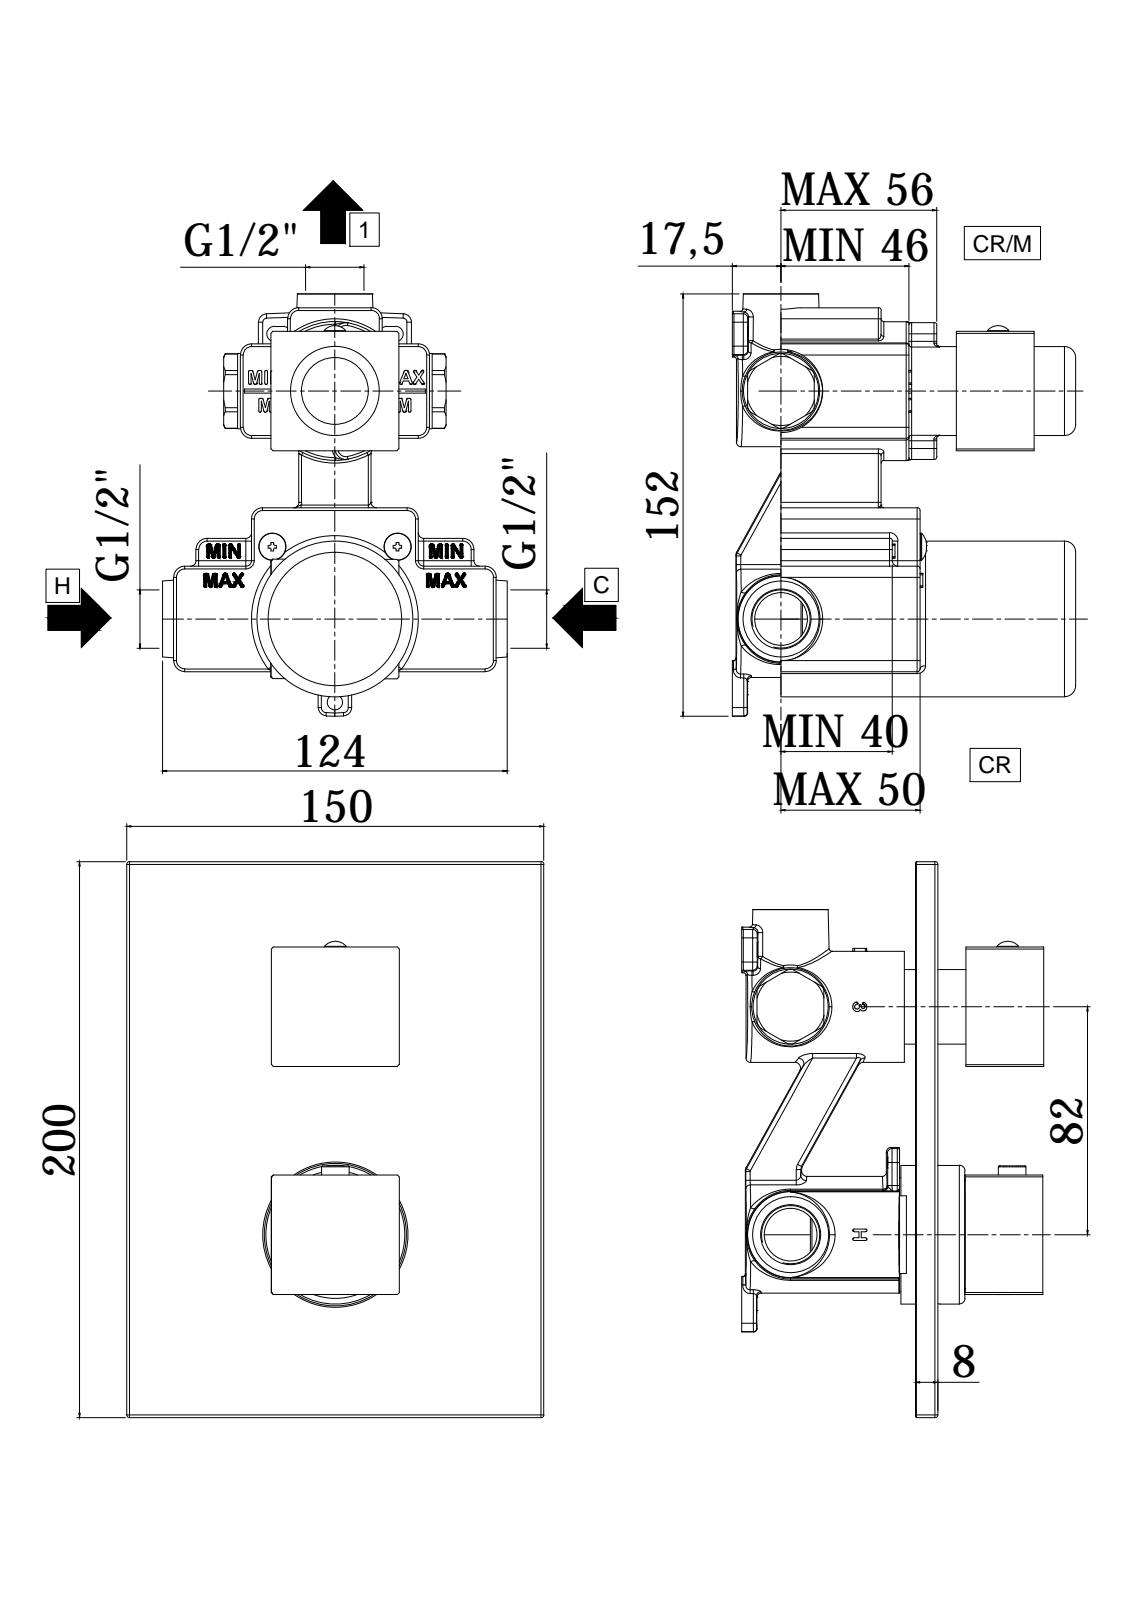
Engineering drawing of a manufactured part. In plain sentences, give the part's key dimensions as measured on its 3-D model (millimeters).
The part is named "LEQ513CR". Its 3-D file was written by "CREO PARAMETRIC BY PTC INC, 2020044 (CONFIG_CONTROL_DESIGN)". It is 1 solid with 68 faces: 20 planar, 32 cylindrical and 16 other. Overall it measures 200 by 150 by 46.21 millimeters. Its volume is 402 004 cubic millimeters and its surface area 81 996 square millimeters. Round bosses or shafts: 2 of diameter 7.6, 1 of diameter 49.9, 1 of diameter 39, 1 of diameter 26.8, 1 of diameter 9.9. Partial cylindrical surfaces (rounded edges, fillets, slot ends): 12 of radius 1, 2 of radius 31. The main face-to-face distances are 9, 52, 98, 43, 82, 46, 45.01, 36.01, 46.21, 37.21.
